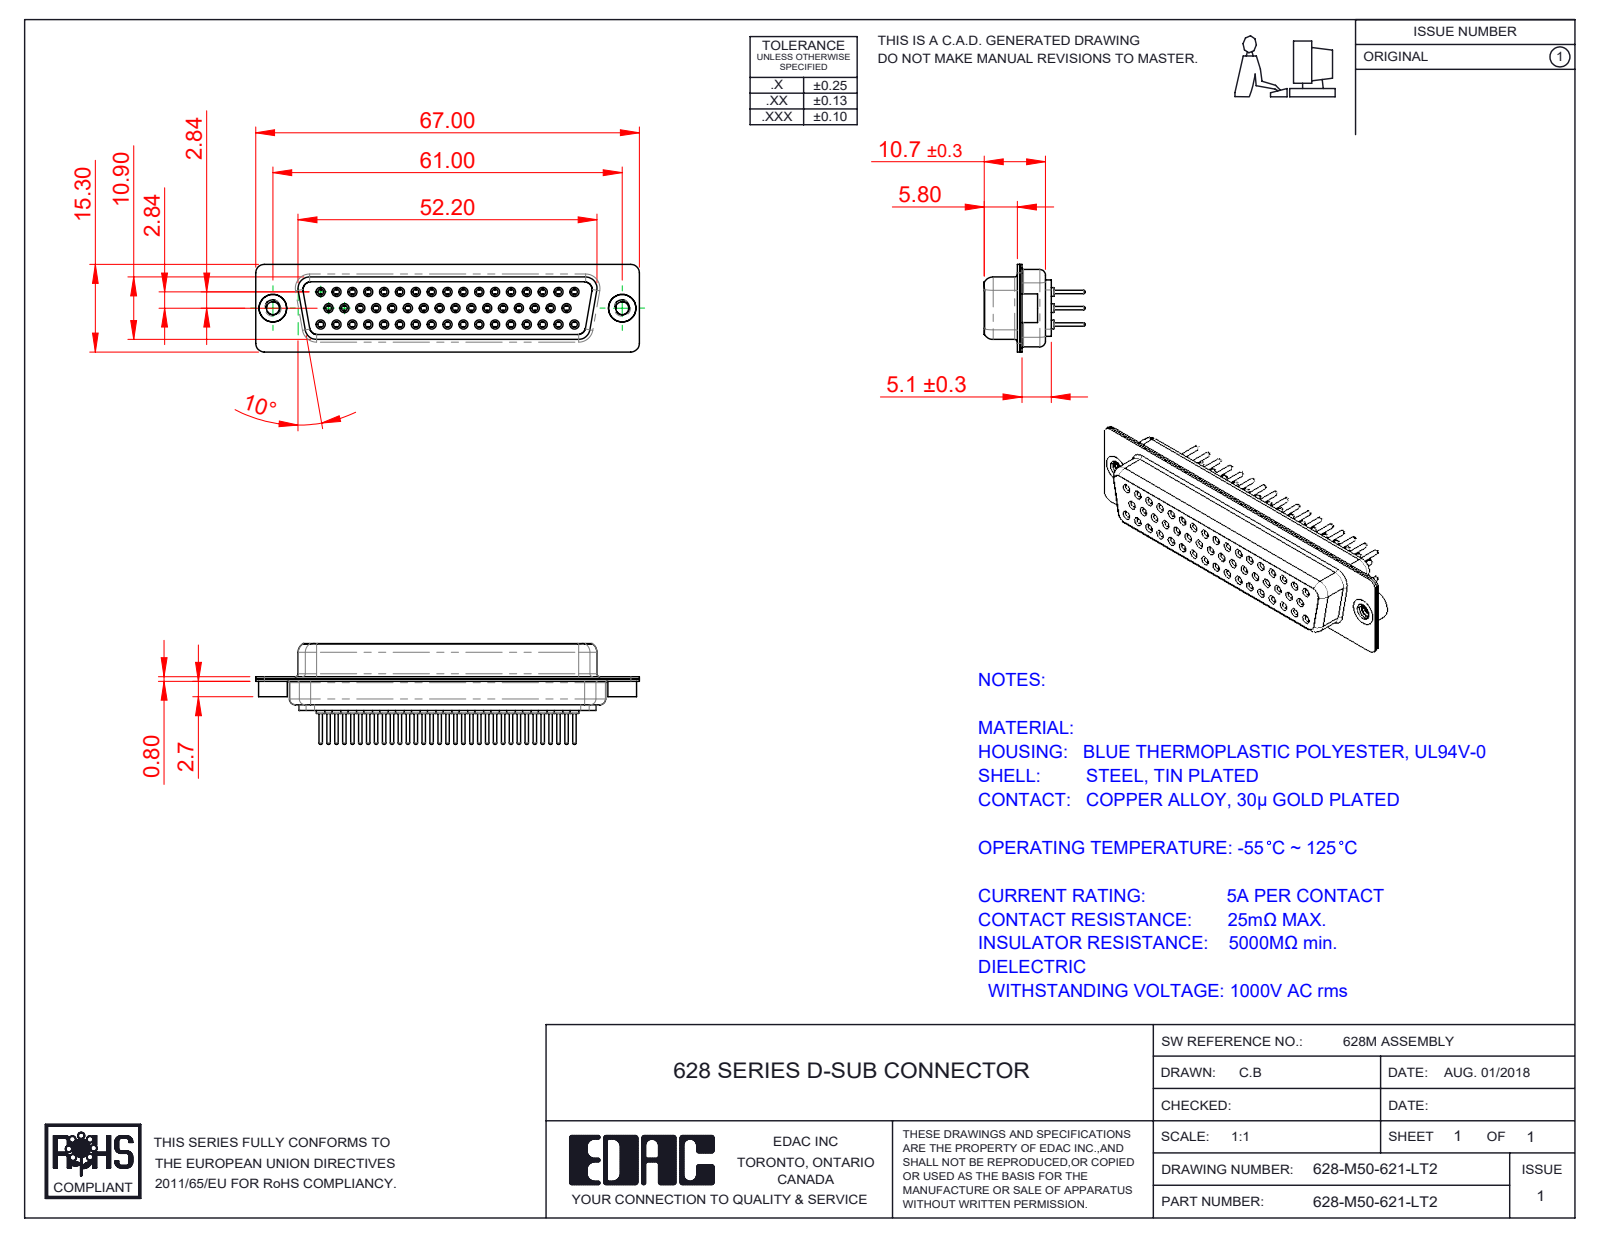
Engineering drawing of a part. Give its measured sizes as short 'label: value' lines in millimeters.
name: 628M Shell Front_50 Contacts; 628M Shell Rear_50 Contacts; 628M Contact Row 1_21; 628M Contact Row 3_21 (+4 more)
written by: SolidWorks 2020 (CONFIG_CONTROL_DESIGN)
unit: mm
bodies: 55 solids, 3029 faces (817 planar, 1087 cylindrical, 1125 other)
size: 67 × 17.6 × 15.3
volume: 6 623 mm³; area: 15 043 mm²
holes: 50× ⌀1, 50× ⌀1.1, 50× ⌀1.7, 50× ⌀1.8, 50× ⌀2, 2× ⌀2.26, 2× ⌀4, 2× ⌀4.8
bosses: 50× ⌀2.2, 50× ⌀1.6, 50× ⌀1.5, 50× ⌀0.6, 2× ⌀5, 2× ⌀4.9
rounds: 16× R1.5, 12× R2, 8× R1.35, 8× R1.6, 4× R0.25, 4× R0.5, 4× R0.6, 4× R0.65
face distances: 0.4, 1.3, 11.8, 0.9, 5.5, 5.9, 0.85, 13.1, 5.8, 10.05
hole spacings: 3.16, 2.77, 5.54, 8.31, 11.08, 13.85, 16.62, 19.39
